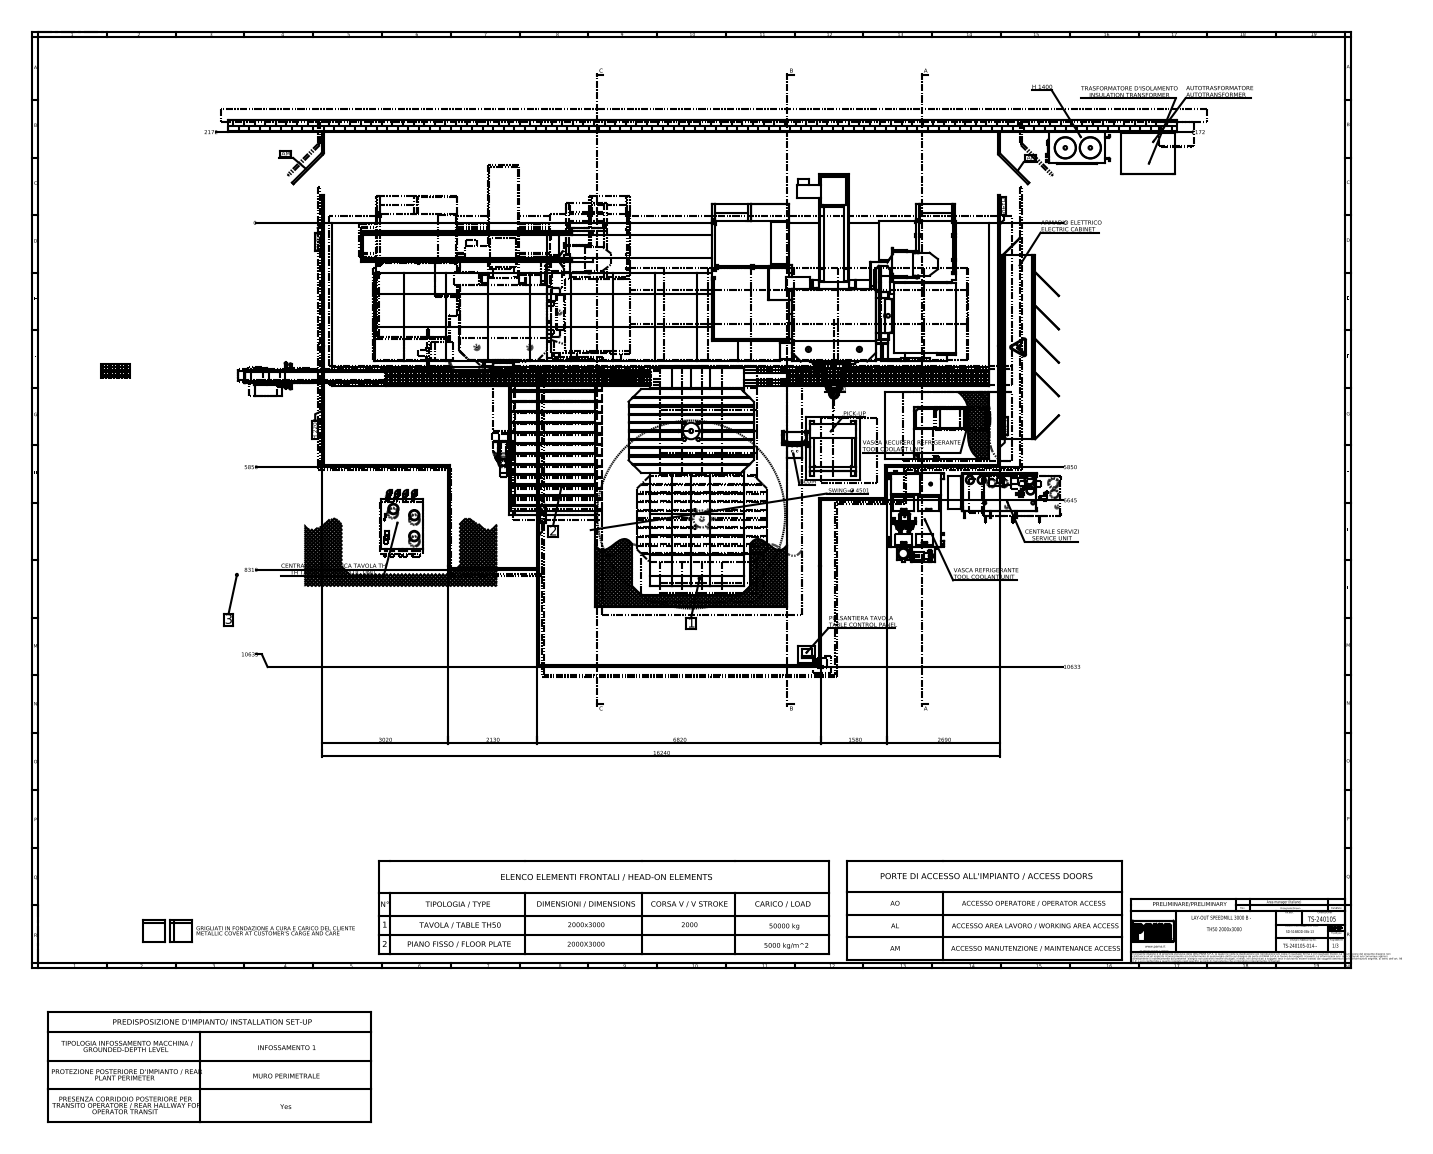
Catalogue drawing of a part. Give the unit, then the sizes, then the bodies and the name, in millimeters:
Units: millimetres
Overall size (bounding box): 22740 × 16055 × 9400
Round holes (diameter × count): ⌀35 ×116, ⌀13 ×16, ⌀14 ×8, ⌀8 ×6, ⌀32 ×6, ⌀12 ×5, ⌀6.8 ×4, ⌀7 ×4, ⌀12.5 ×4, ⌀56.66 ×3, ⌀4.2 ×2, ⌀9 ×2
Round bosses / shafts (diameter × count): ⌀20 ×14, ⌀60 ×10, ⌀9 ×10, ⌀80 ×9, ⌀200 ×8, ⌀55 ×8, ⌀30 ×8, ⌀66.3 ×7
Partial cylindrical surfaces — rounded edges, fillets, slot ends (radius × count): R5 ×241, R10 ×83, R6 ×37, R2 ×30, R15 ×26, R20 ×26, R3 ×14, R24 ×14
Main face-to-face distances: 2000, 300, 50, 450, 1550, 16055, 15755, 22740, 150, 100
Hole centre spacings: 250, 500, 750, 1000, 1250, 1500, 1750, 2000
Volume: 767 600 000 000 mm³ · Surface area: 2 401 000 000 mm²
Bodies: 540 solids, 7858 faces (5924 planar, 1505 cylindrical, 429 other)
Part name (STEP PRODUCT): S001560_4 (3+1) POSTI; LAYOUT SPEEDMILL PMS V2.0; S002740_PEDANA RITRATTA - PORTE CHIUSE; S000047 (+8 more)
STEP written by: SolidWorks 2023 (AUTOMOTIVE_DESIGN)
